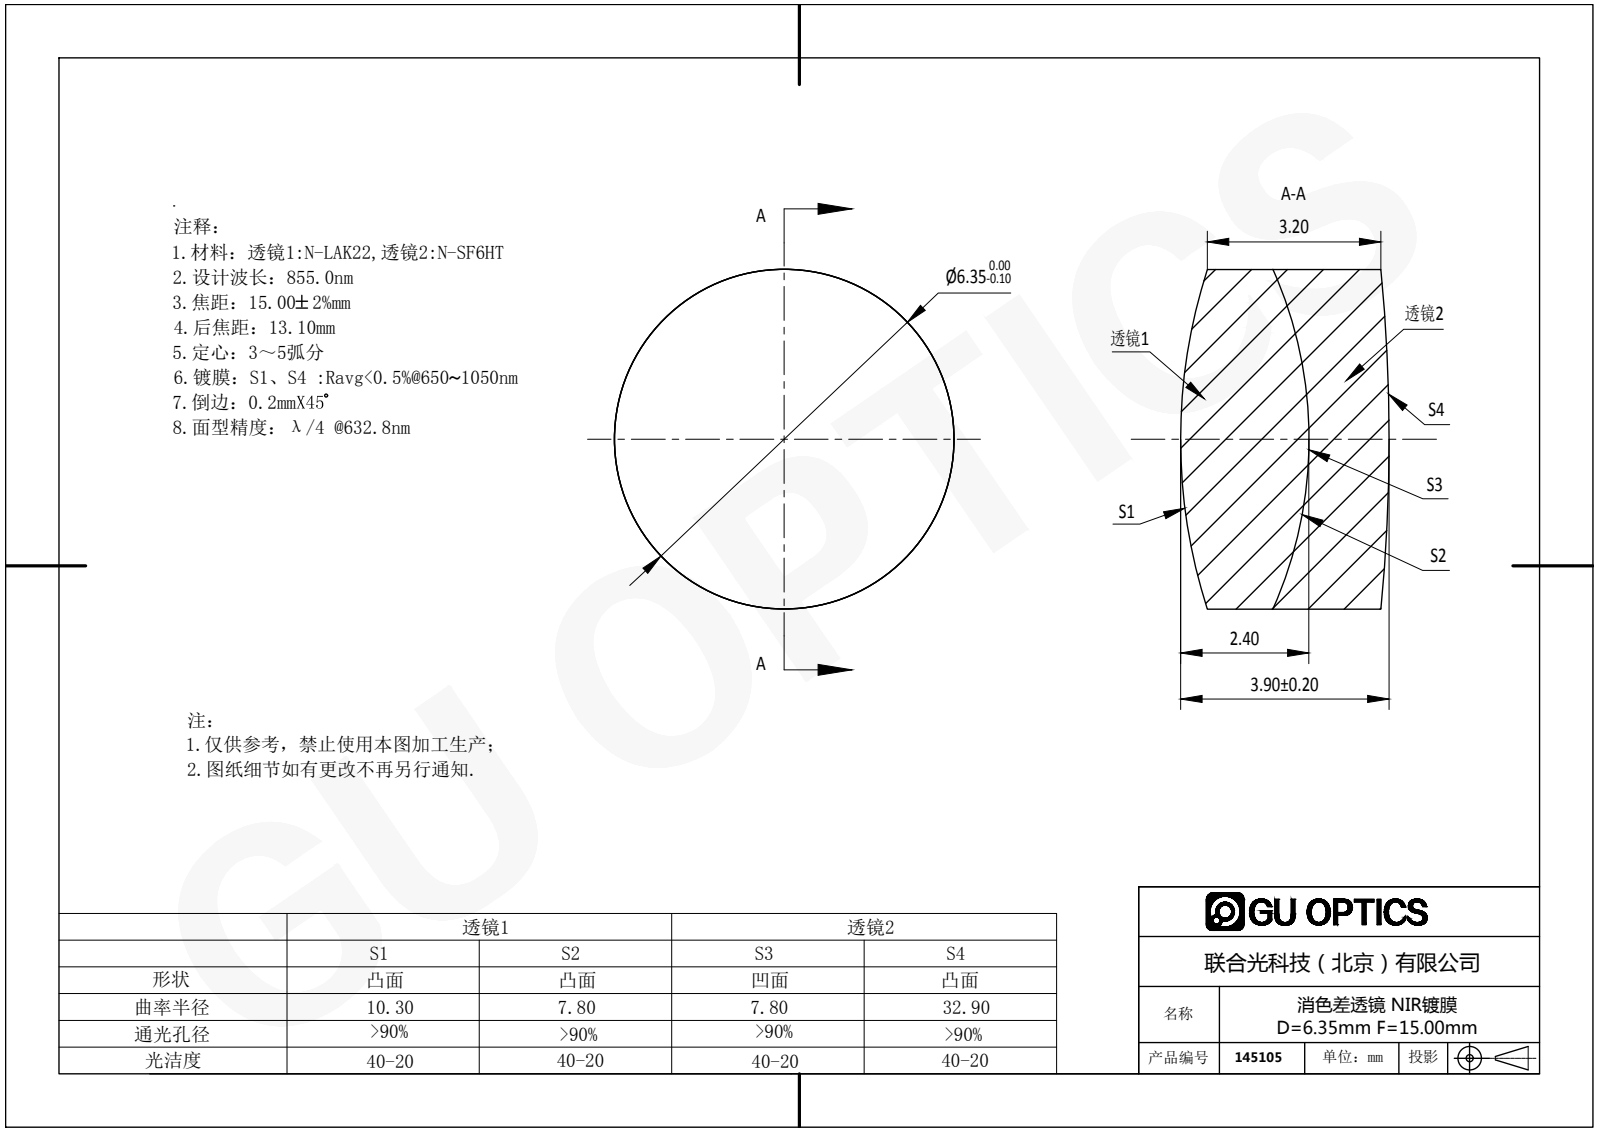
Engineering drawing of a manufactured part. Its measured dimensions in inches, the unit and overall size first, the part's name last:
Units: inches
Overall size (bounding box): 0.25 × 0.25 × 0.154
Round bosses / shafts (diameter × count): ⌀0.25 ×1
Volume: 0.007 in³ · Surface area: 0.302 in²
Bodies: 2 solids, 12 faces (0 planar, 4 cylindrical, 8 other)
Part name (STEP PRODUCT): 145105
STEP written by: SolidWorks 2016 (AUTOMOTIVE_DESIGN)
